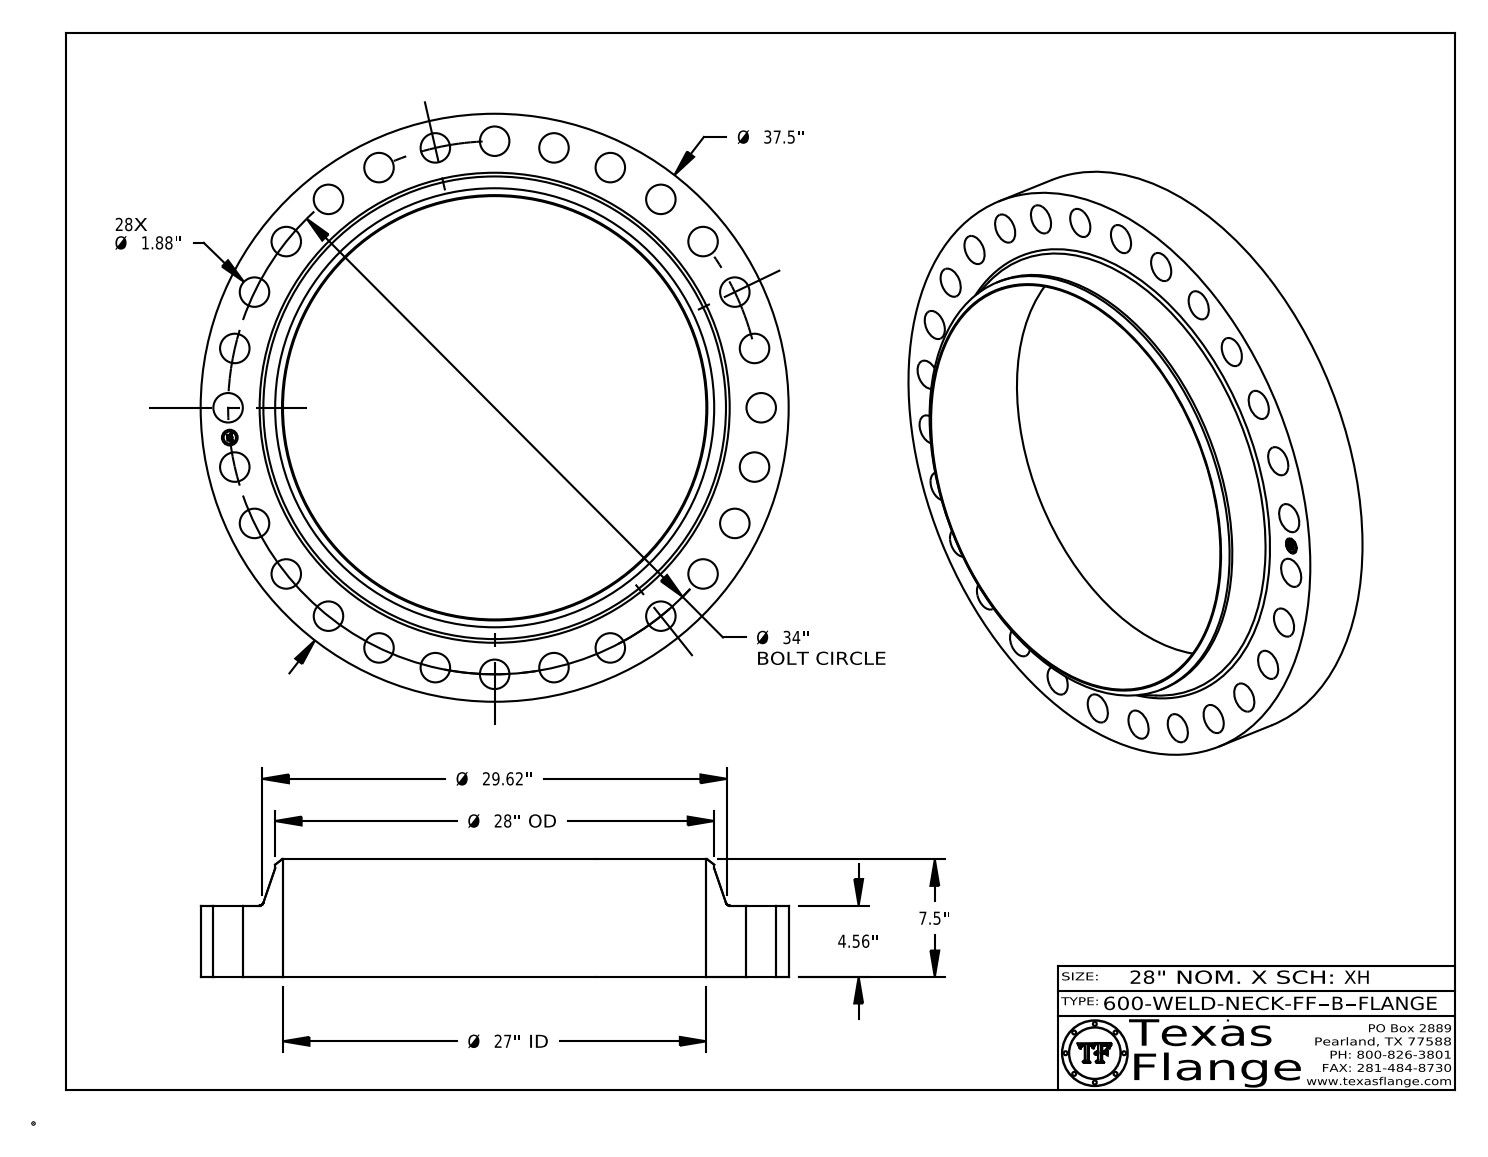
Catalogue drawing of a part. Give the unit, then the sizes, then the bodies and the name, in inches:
Units: inches
Overall size (bounding box): 37.5 × 37.5 × 7.5
Round holes (diameter × count): ⌀1.88 ×28, ⌀1 ×1, ⌀27 ×1
Round bosses / shafts (diameter × count): ⌀0.061 ×8, ⌀37.5 ×1, ⌀28 ×1, ⌀0.788 ×1
Main face-to-face distances: 4.56, 7.5, 2.94, 0.015, 4.545, 2.955, 0.298, 0.293, 0.054, 0.193
Hole centre spacings: 3.807, 7.566, 30.633, 33.786, 17, 11.23, 18.089, 21.198
Volume: 2 278 in³ · Surface area: 3 016 in²
Bodies: 1 solid, 456 faces (368 planar, 82 cylindrical, 6 other)
Part name (STEP PRODUCT): 600-WELD-NECK-FF, Series B
STEP written by: CATIA V5 STEP AP214 (AUTOMOTIVE_DESIGN)
